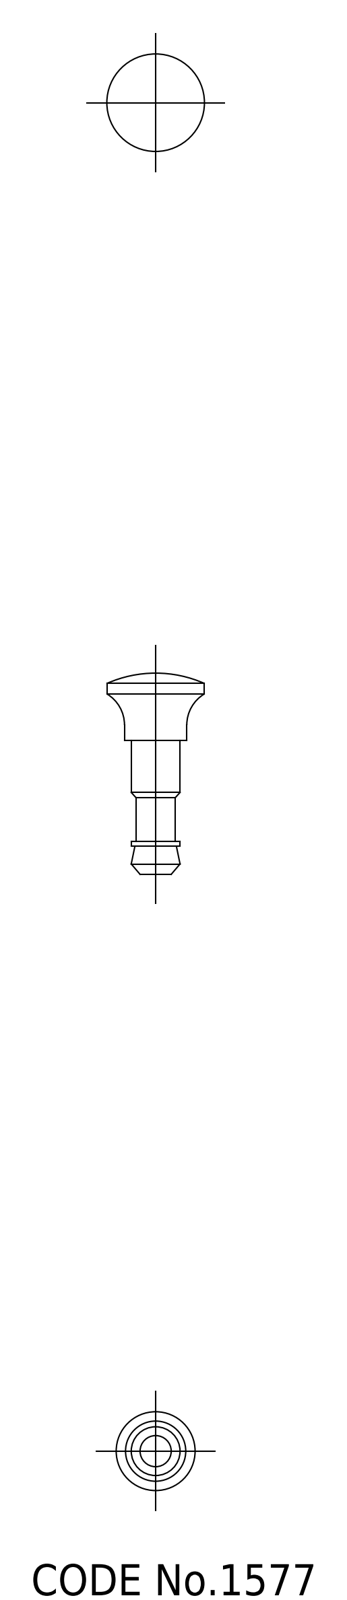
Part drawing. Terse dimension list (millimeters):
name: plunger
written by: CADfix (AUTOMOTIVE_DESIGN)
unit: mm
bodies: 1 solid, 23 faces (0 planar, 0 cylindrical, 23 other)
size: 19.4 × 9.4 × 9.4
volume: 452 mm³; area: 421 mm²
